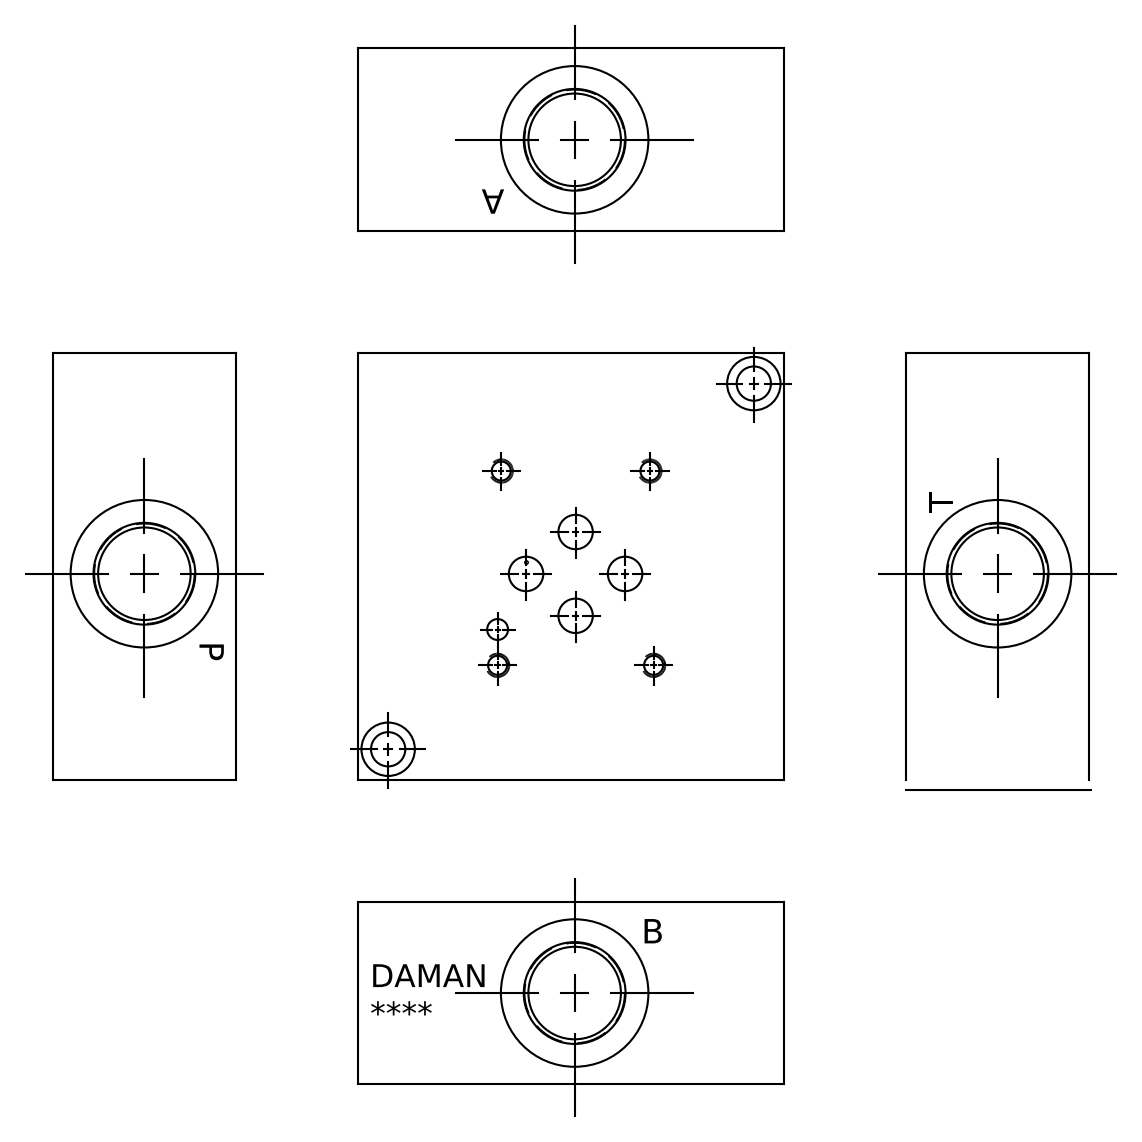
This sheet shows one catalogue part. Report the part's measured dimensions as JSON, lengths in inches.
{"part_name": "Part__D03SPS8B_3D", "step_written_by": "Autodesk Inventor 2020 (AUTOMOTIVE_DESIGN)", "units": "inches", "bodies": {"solids": 1, "faces": 468, "planar": 276, "cylindrical": 33, "other": 159}, "overall_size": [3.5, 3.5, 1.5], "volume_in3": 15.94, "surface_area_in2": 60.5, "round_holes": [[0.149, 4], [0.19, 4], [0.28, 4], [0.282, 2], [0.406, 2], [0.625, 2], [0.745, 2], [0.829, 2], [1.208, 2], [0.156, 1]], "face_to_face_distances": [1.5, 3.5, 0.031, 3.469, 3.438, 0.653, 0.684, 2.816, 2.785, 2.132], "hole_center_spacings": [0.532, 0.533, 0.785, 0.868, 1.288, 1.321, 1.594, 2.026]}
